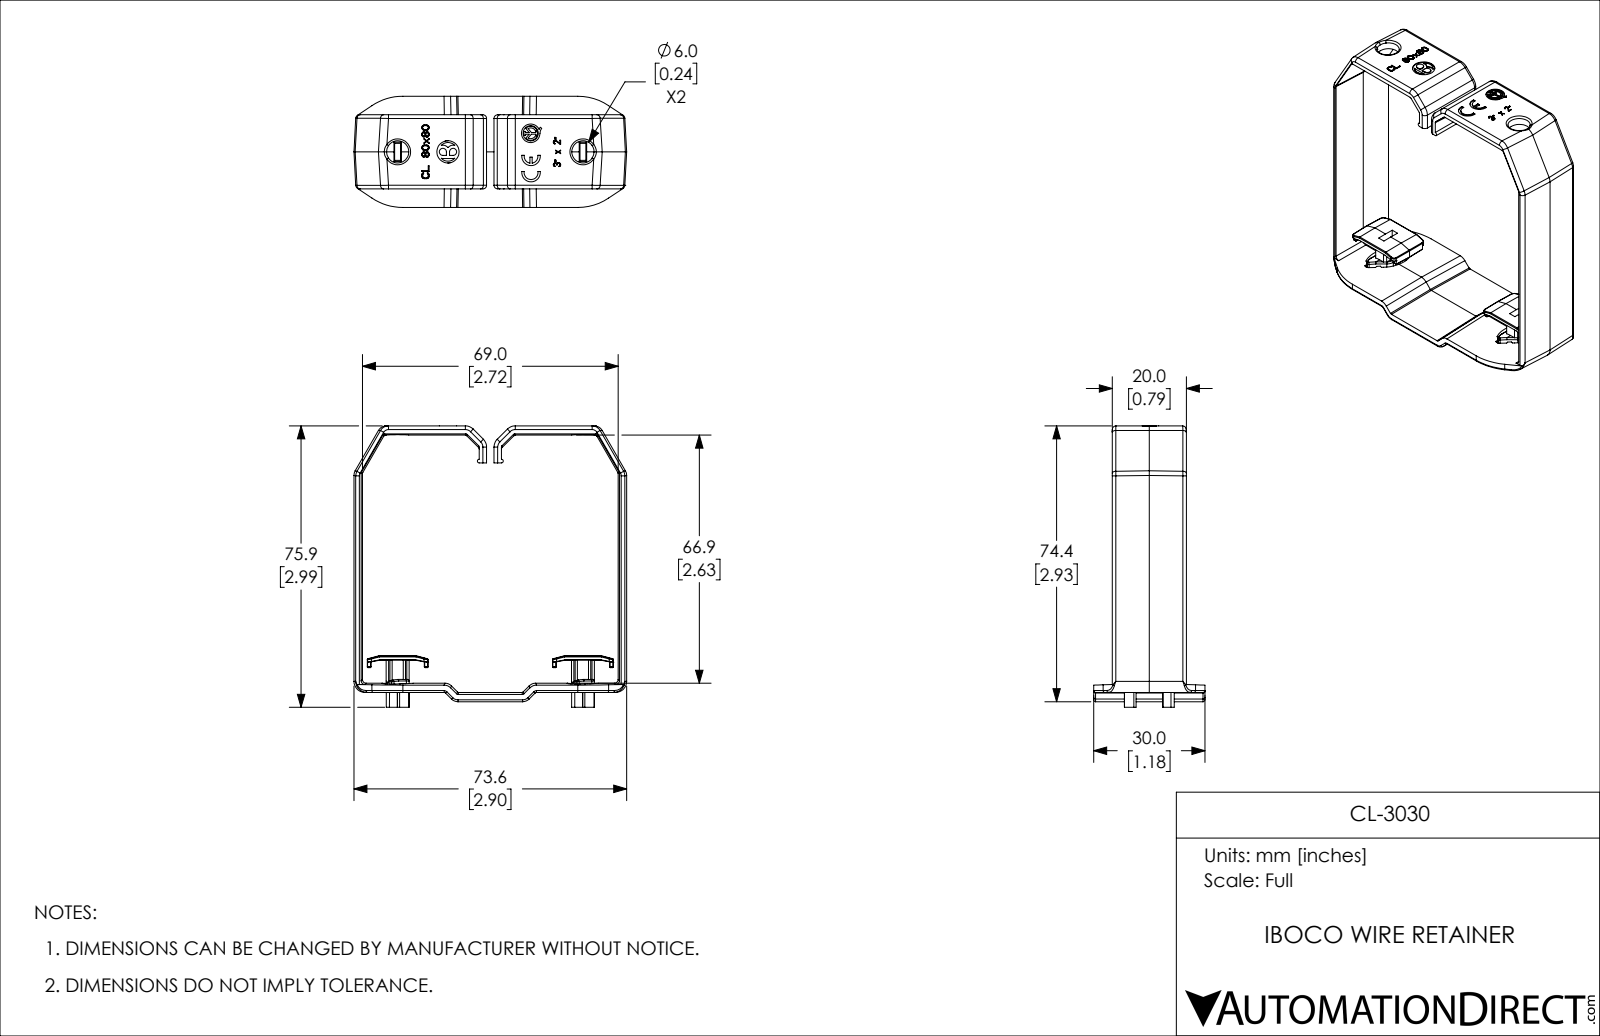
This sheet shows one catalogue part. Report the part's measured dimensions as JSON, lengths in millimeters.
{"part_name": "CL-3030", "step_written_by": "SolidWorks 2019 (CONFIG_CONTROL_DESIGN)", "units": "millimeters", "bodies": {"solids": 1, "faces": 1003, "planar": 681, "cylindrical": 255, "other": 67}, "overall_size": [75.9, 73.6, 30], "volume_mm3": 13200, "surface_area_mm2": 15090, "round_holes": [[6, 3], [5, 1]], "round_bosses_or_shafts": [[4.1, 1]], "partial_cylinders_radius": [[0.5, 48], [0.2, 36], [1, 34], [2.5, 20], [0.3, 12], [0.4, 12], [3, 8], [0.7, 4]], "face_to_face_distances": [68.9, 2.5, 73.5, 66.8, 71.9, 69.3, 74.4, 2, 4, 1.2], "hole_center_spacings": [13.6, 15, 22.9, 36.2, 36.4, 50]}
